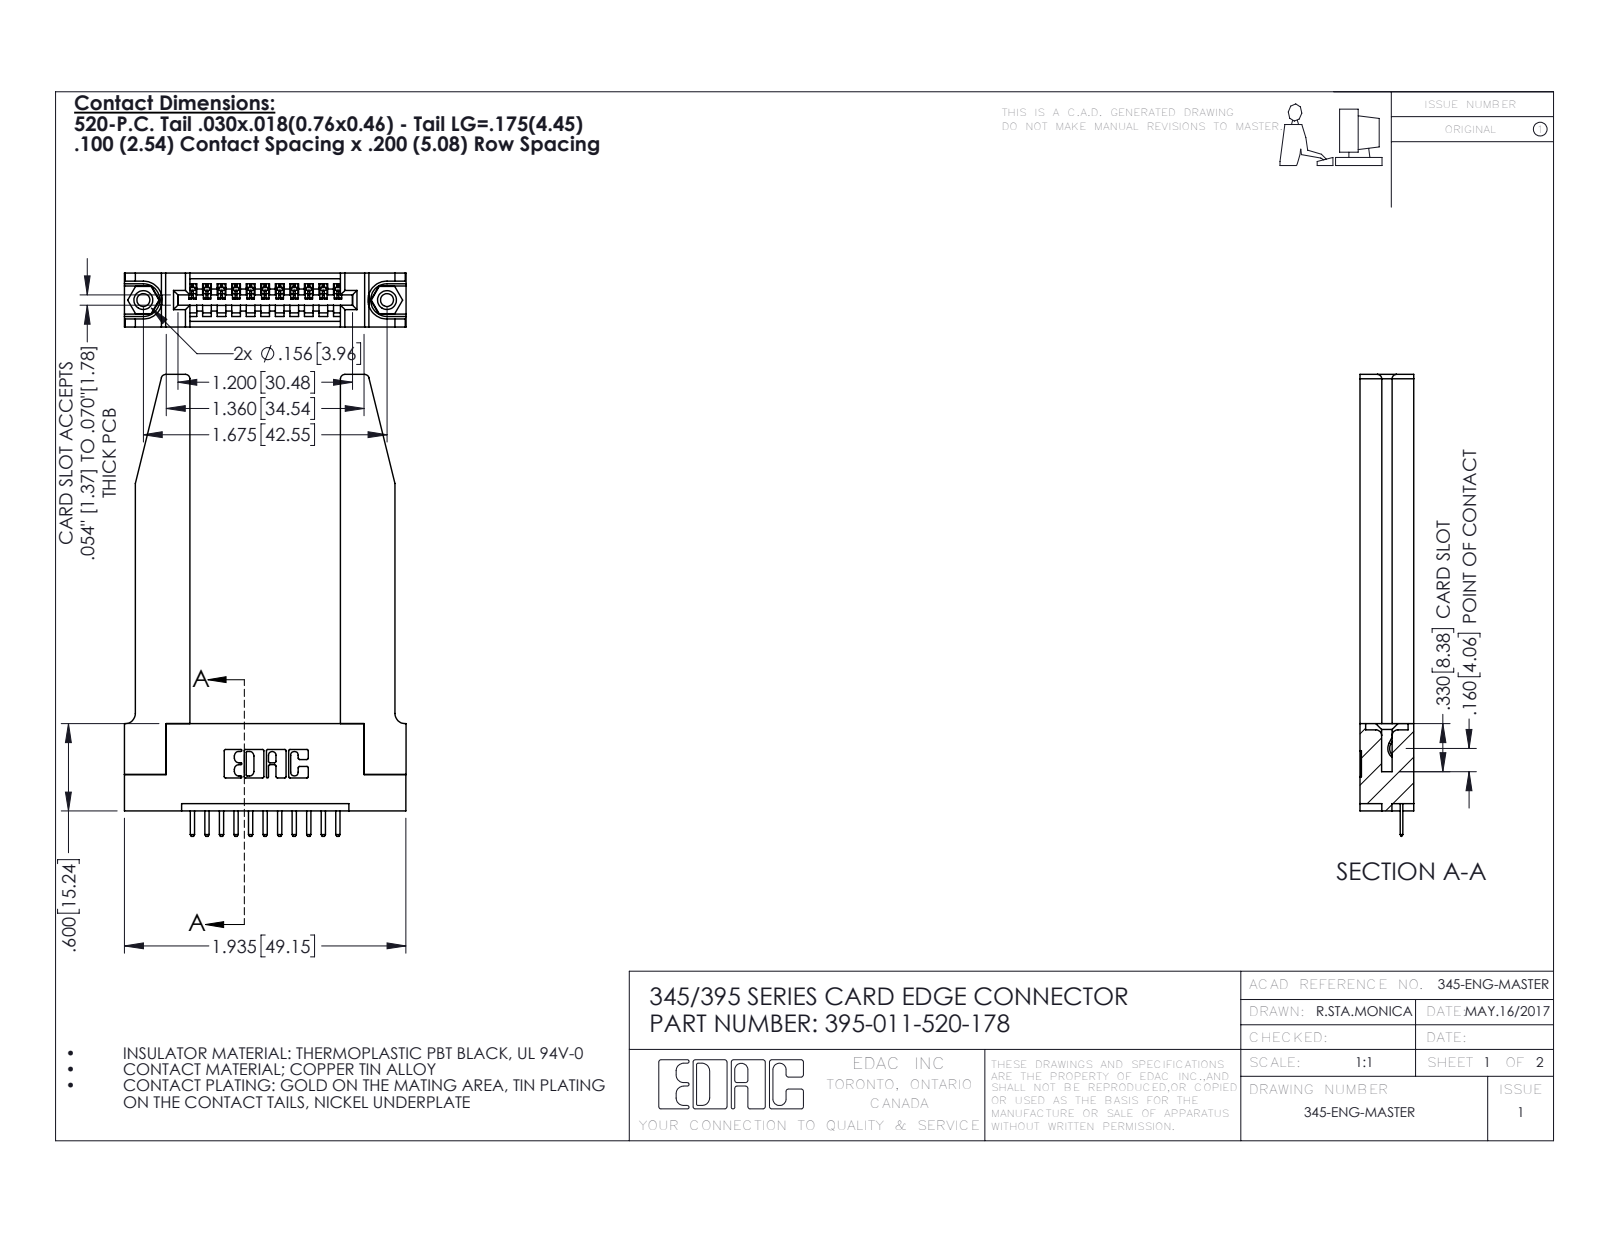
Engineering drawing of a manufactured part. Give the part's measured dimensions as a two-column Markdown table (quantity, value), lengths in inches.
| quantity | value |
| --- | --- |
| part name | 345-292-001_345-293-120; 395-011-520-178; 345 Part_Flush Mounting Lugs - 0.156 Dia-TH; 345-220-078_345-220-078 (+1 more) |
| STEP written by | SolidWorks 2016 (CONFIG_CONTROL_DESIGN) |
| units | inches |
| bodies | 16 solids, 1042 faces (684 planar, 306 cylindrical, 52 other) |
| overall size | 3.175 × 1.936 × 0.37 |
| volume | 0.742 in³ |
| surface area | 18.83 in² |
| round holes (diameter × count) | 0.089 × 2, 0.125 × 2, 0.156 × 2, 0.064 × 1 |
| round bosses / shafts (diameter × count) | 0.155 × 2 |
| partial cylindrical surfaces (radius × count) | 0.01 × 24, 0.006 × 22, 0.01 × 22, 0.03 × 8, 0.007 × 6, 0.031 × 6, 0.026 × 3, 0.031 × 2 |
| main face-to-face distances | 0.37, 0.072, 0.298, 0.148, 0.15, 0.2, 0.077, 0.22, 1.035, 0.095 |
| hole center spacings | 0.27, 1.443, 1.675 |
